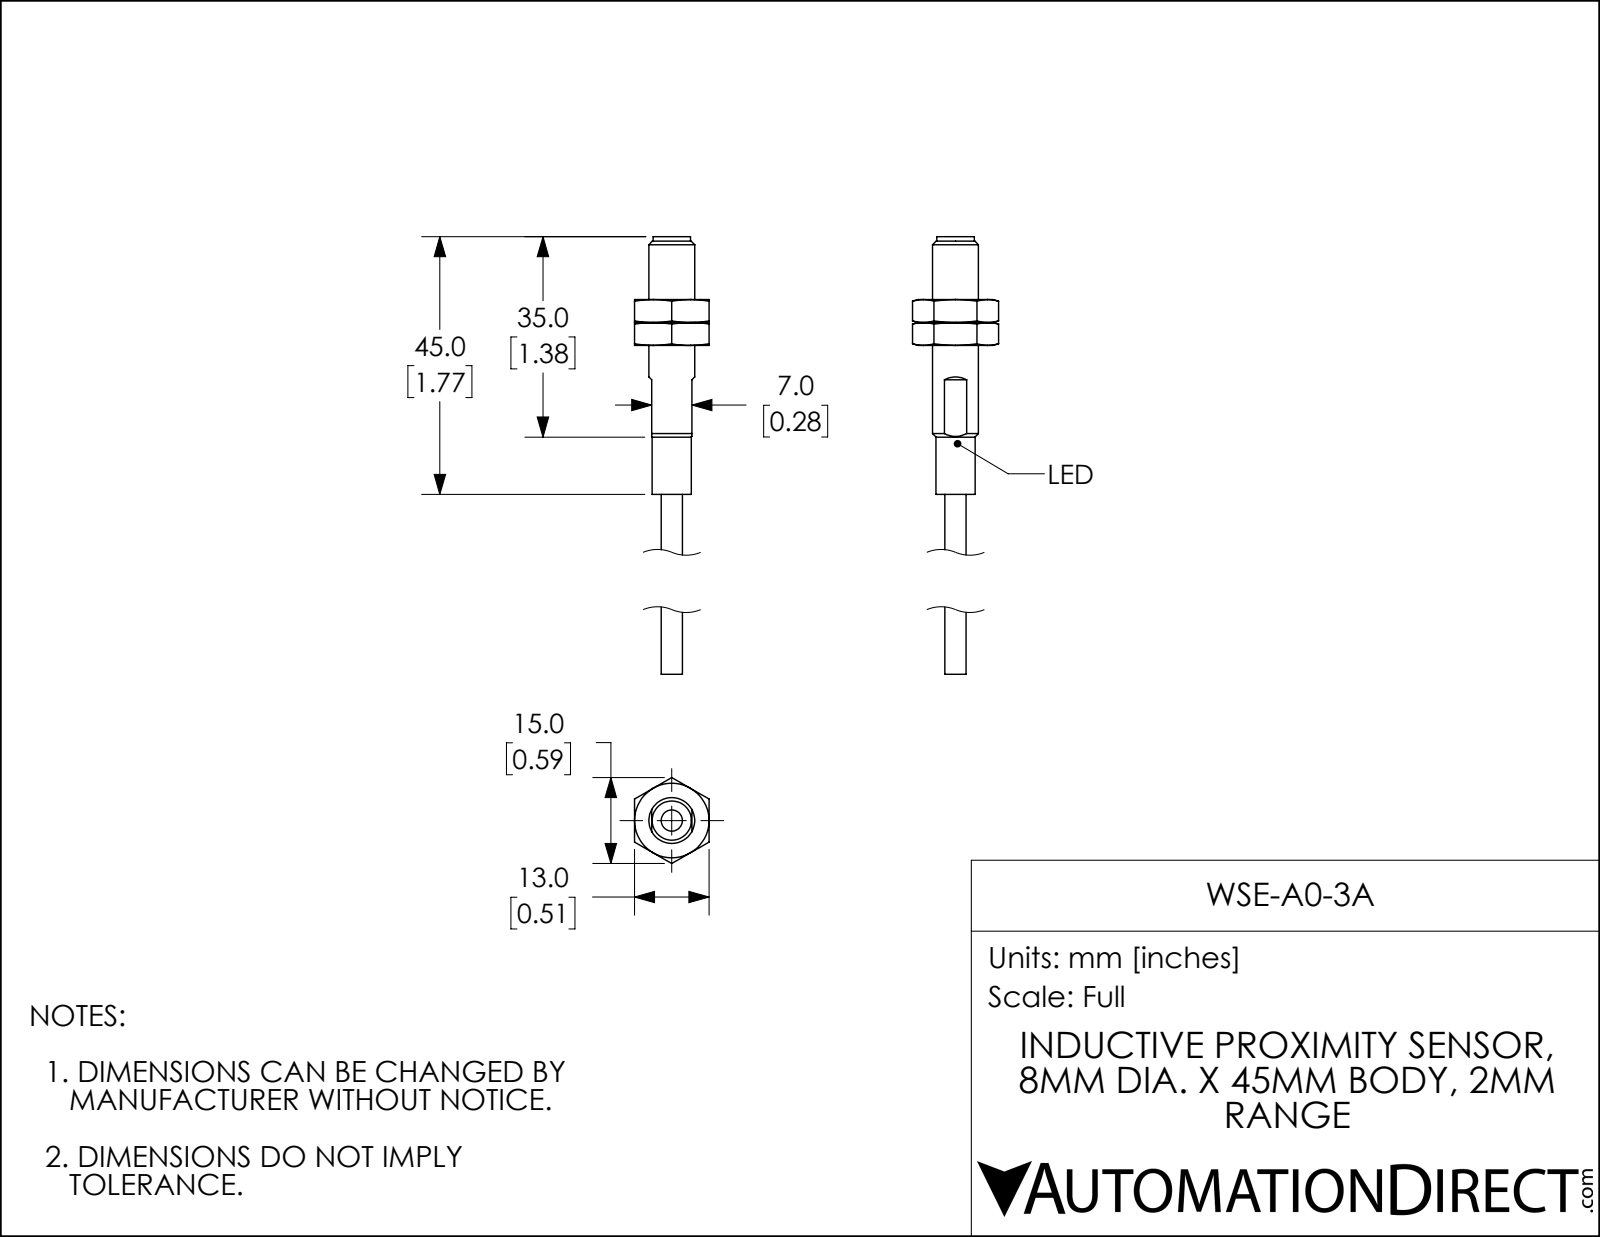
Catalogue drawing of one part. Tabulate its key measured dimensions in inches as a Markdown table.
| quantity | value |
| --- | --- |
| part name | WSE-A0-3A |
| STEP written by | SolidWorks 2017 (AUTOMOTIVE_DESIGN) |
| units | inches |
| bodies | 3 solids, 61 faces (25 planar, 6 cylindrical, 30 other) |
| overall size | 3.774 × 0.591 × 0.512 |
| volume | 0.212 in³ |
| surface area | 4.17 in² |
| round holes (diameter × count) | 0.272 × 1 |
| round bosses / shafts (diameter × count) | 0.315 × 1, 0.27 × 1, 0.258 × 1, 0.146 × 1 |
| main face-to-face distances | 0.512, 0.157, 0.315, 0.394, 0.118, 0.276, 0.748, 0.591, 0.433, 1.024 |
